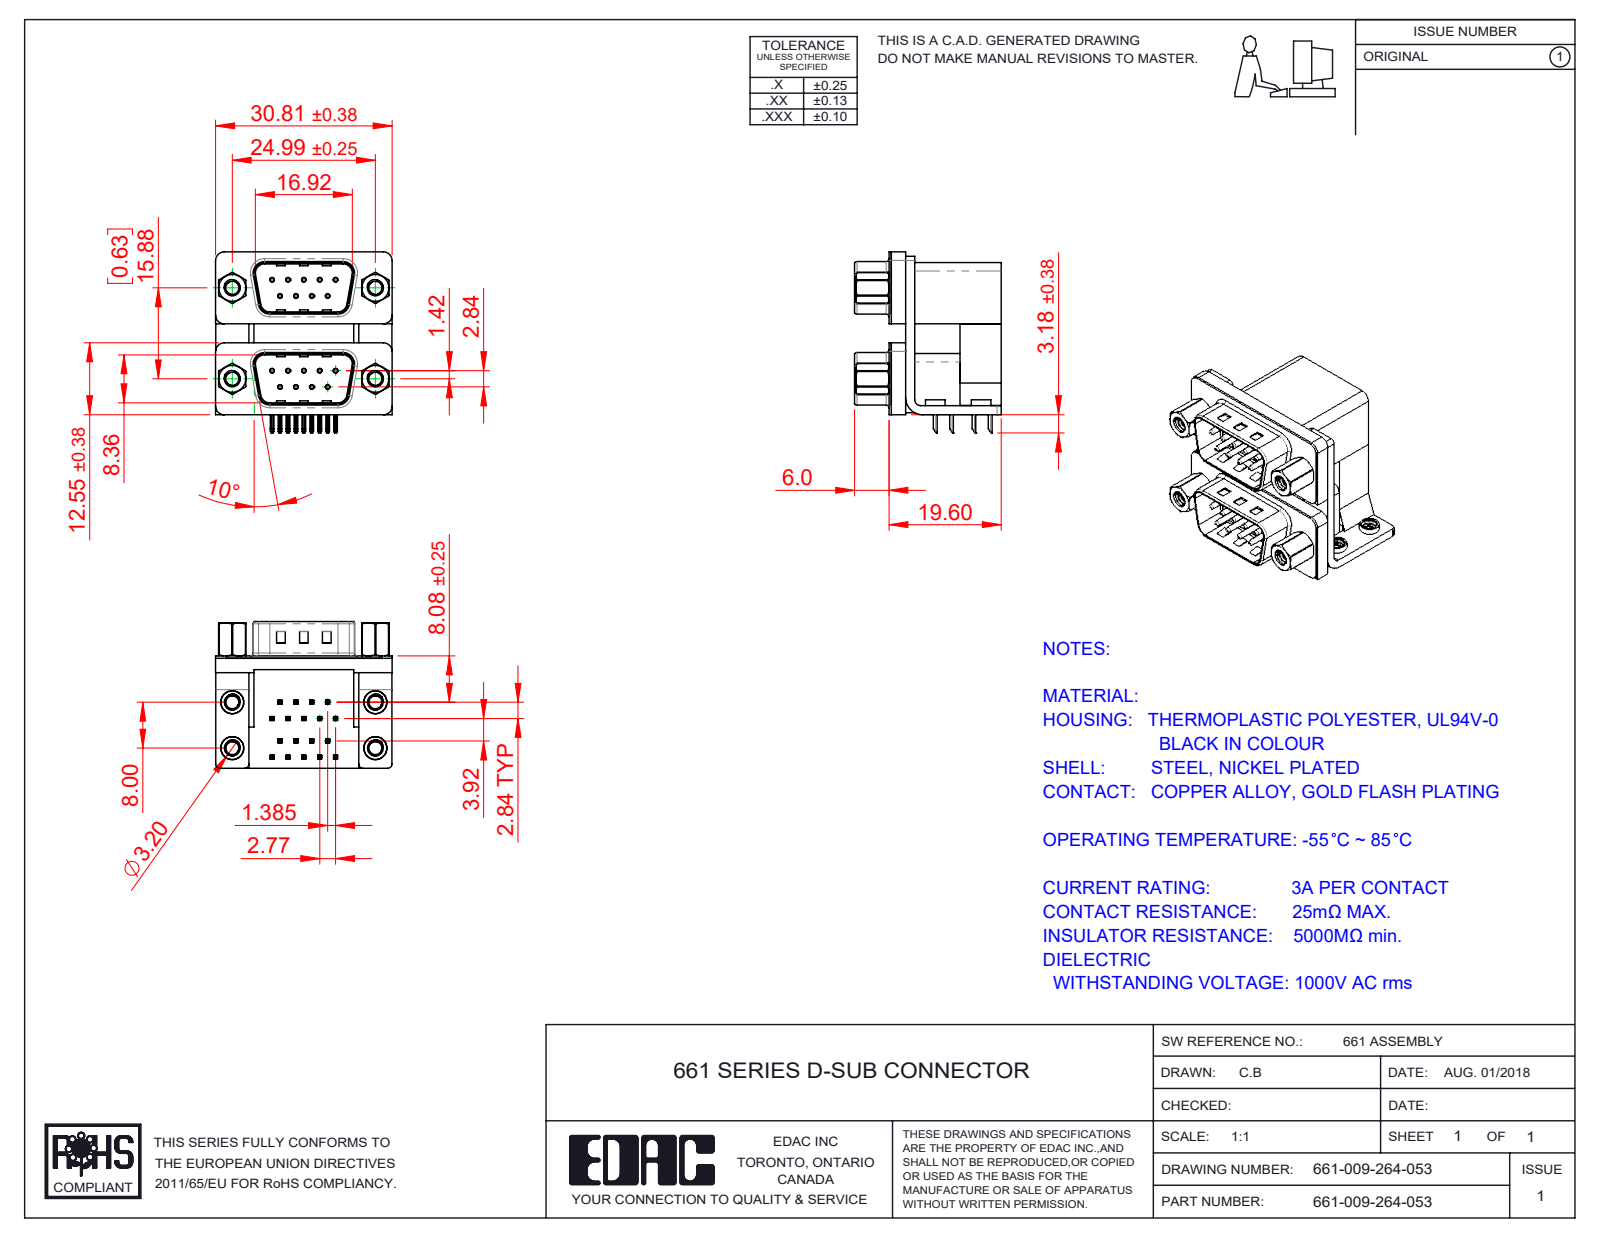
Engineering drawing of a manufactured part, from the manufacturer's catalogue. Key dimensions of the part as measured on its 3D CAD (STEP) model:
Part name (STEP PRODUCT): 661 Contact Top Upper_L; 661 4-40 Threaded Board Mount; 661-009-264-053; 661 Contact Top Lower (+8 more)
STEP written by: SolidWorks 2020 (CONFIG_CONTROL_DESIGN)
Units: millimetres
Bodies: 37 solids, 2340 faces (1208 planar, 814 cylindrical, 318 other)
Overall size (bounding box): 31.61 × 30.81 × 25.6
Volume: 10 297 mm³ · Surface area: 12 623 mm²
Round holes (diameter × count): ⌀0.35 ×18, ⌀0.8 ×18, ⌀2.26 ×8, ⌀2.29 ×4, ⌀2.75 ×4, ⌀3.2 ×4, ⌀3.5 ×4, ⌀4 ×4, ⌀4.8 ×4, ⌀5 ×4
Round bosses / shafts (diameter × count): ⌀0.75 ×18, ⌀4.9 ×4, ⌀4.75 ×4, ⌀4 ×4, ⌀3.9 ×4, ⌀3.4 ×4, ⌀2.79 ×4
Partial cylindrical surfaces — rounded edges, fillets, slot ends (radius × count): R0.25 ×72, R0.12 ×36, R0.5 ×16, R1.5 ×13, R0.75 ×8, R0.9 ×8, R1.6 ×8, R2 ×8
Main face-to-face distances: 0.4, 2.5, 16.7, 19.2, 15.87, 19.6, 2.9, 1.6, 7.2, 9.5
Hole centre spacings: 3.16, 16.12, 2.77, 15.88, 16.82, 18.77, 5.54, 24.99
